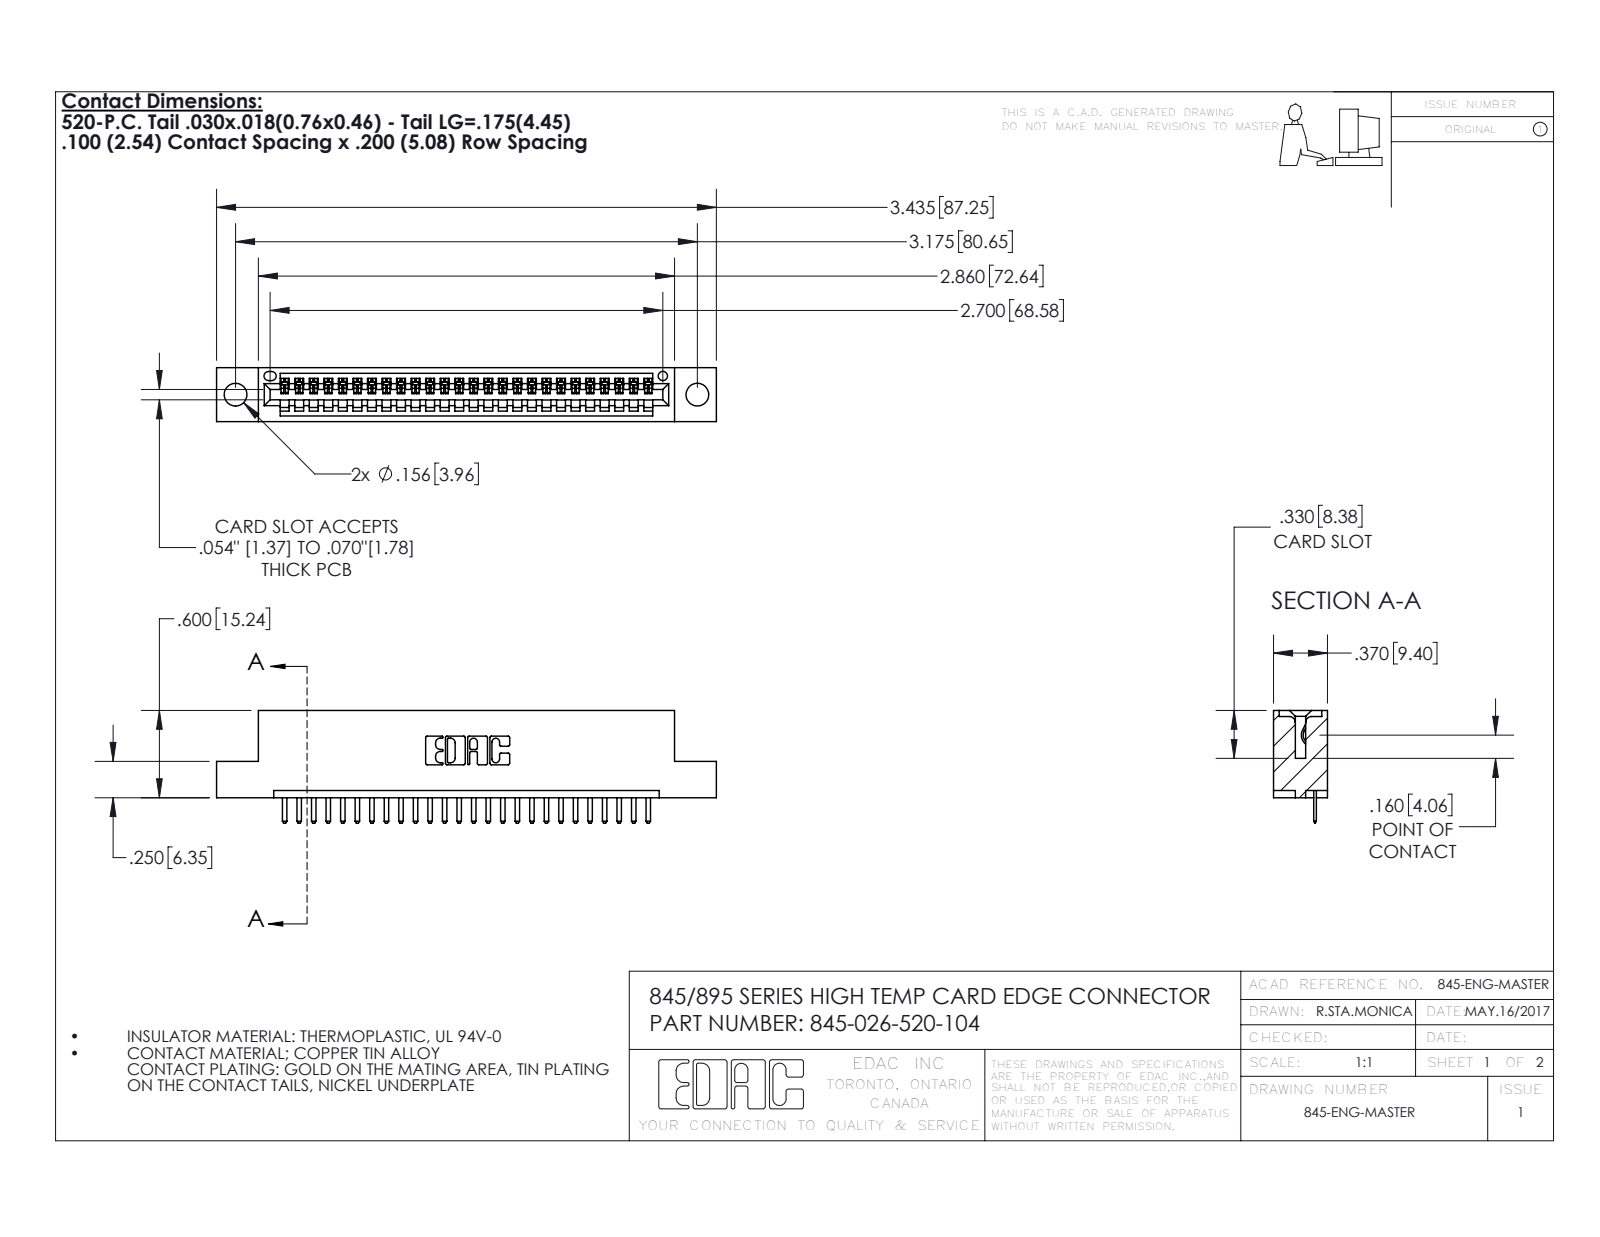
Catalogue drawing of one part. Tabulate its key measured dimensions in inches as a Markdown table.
| quantity | value |
| --- | --- |
| part name | 345 Part_Flush Mounting Lugs - 0.156 Dia-TH; 345-292-001_345-293-120; 345-026-520-104 |
| STEP written by | SolidWorks 2016 (CONFIG_CONTROL_DESIGN) |
| units | inches |
| bodies | 27 solids, 1738 faces (1172 planar, 566 cylindrical, 0 other) |
| overall size | 3.435 × 0.775 × 0.37 |
| volume | 0.488 in³ |
| surface area | 15.45 in² |
| round holes (diameter × count) | 0.156 × 2, 0.064 × 1 |
| partial cylindrical surfaces (radius × count) | 0.01 × 54, 0.006 × 52, 0.01 × 22, 0.007 × 6, 0.031 × 6, 0.026 × 3, 0.031 × 2, 0.04 × 2 |
| main face-to-face distances | 0.298, 0.072, 0.37, 0.2, 0.098, 0.272, 0.025, 0.225, 0.072, 0.149 |
| hole center spacings | 0.27, 2.94, 3.175 |
